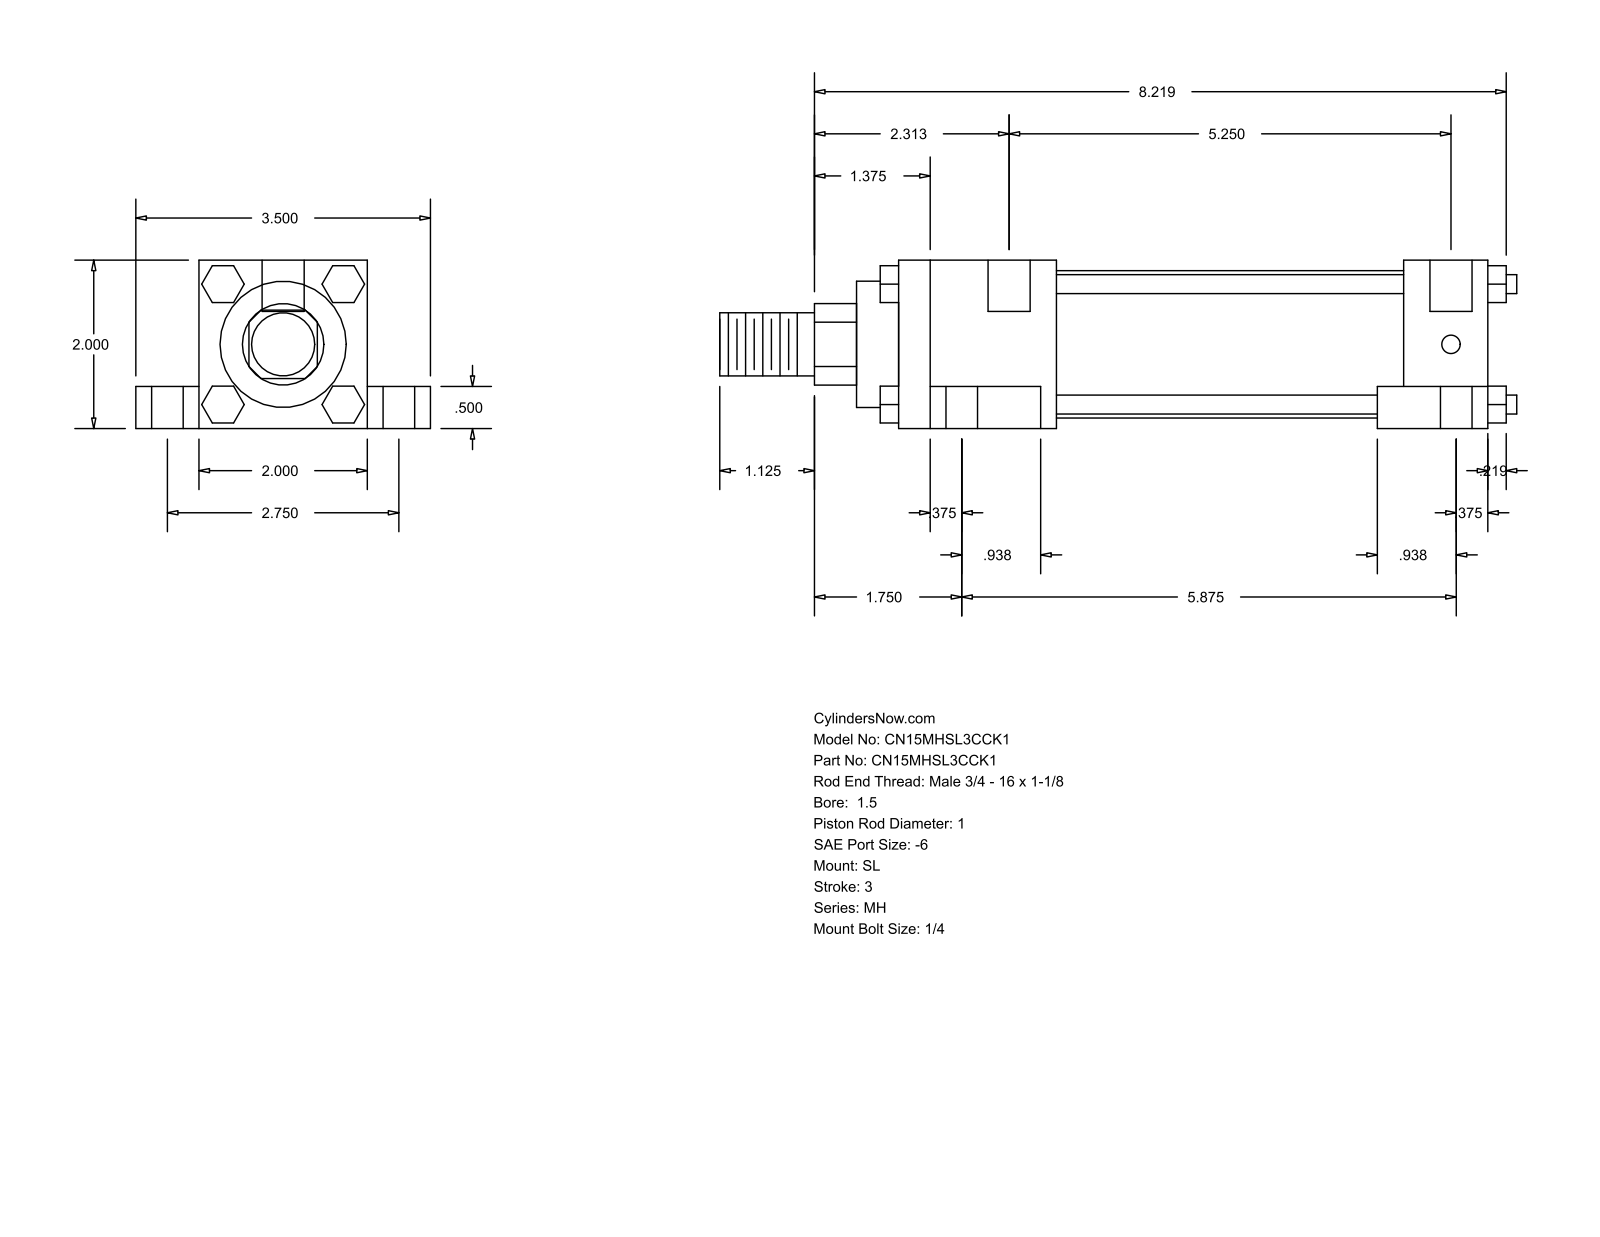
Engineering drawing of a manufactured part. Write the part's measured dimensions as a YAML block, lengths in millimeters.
part_name: "MH_SL__0150_1"
step_written_by: "GSSL Pune (CONFIG_CONTROL_DESIGN)"
units: millimeters
bodies: {solids: 0, faces: 148, planar: 112, cylindrical: 36, other: 0}
overall_size: [240.51, 88.9, 50.8]
round_holes:
  - {diameter: 5.56, count: 4}
  - {diameter: 9.53, count: 4}
  - {diameter: 15.88, count: 4}
  - {diameter: 12.7, count: 2}
round_bosses_or_shafts:
  - {diameter: 5.71, count: 4}
  - {diameter: 44.45, count: 1}
  - {diameter: 38.1, count: 1}
  - {diameter: 25.4, count: 1}
  - {diameter: 19.05, count: 1}
partial_cylinders:
  - {radius: 12.29, count: 1}
face_to_face_distances: [50.8, 12.7, 38.1, 19.05, 69.85, 177.8, 25.4, 9.52, 33.34, 134.94]
hole_center_spacings: [34.96, 36.64, 37.73, 69.84, 136.53, 139.39, 142.47, 149.23]
